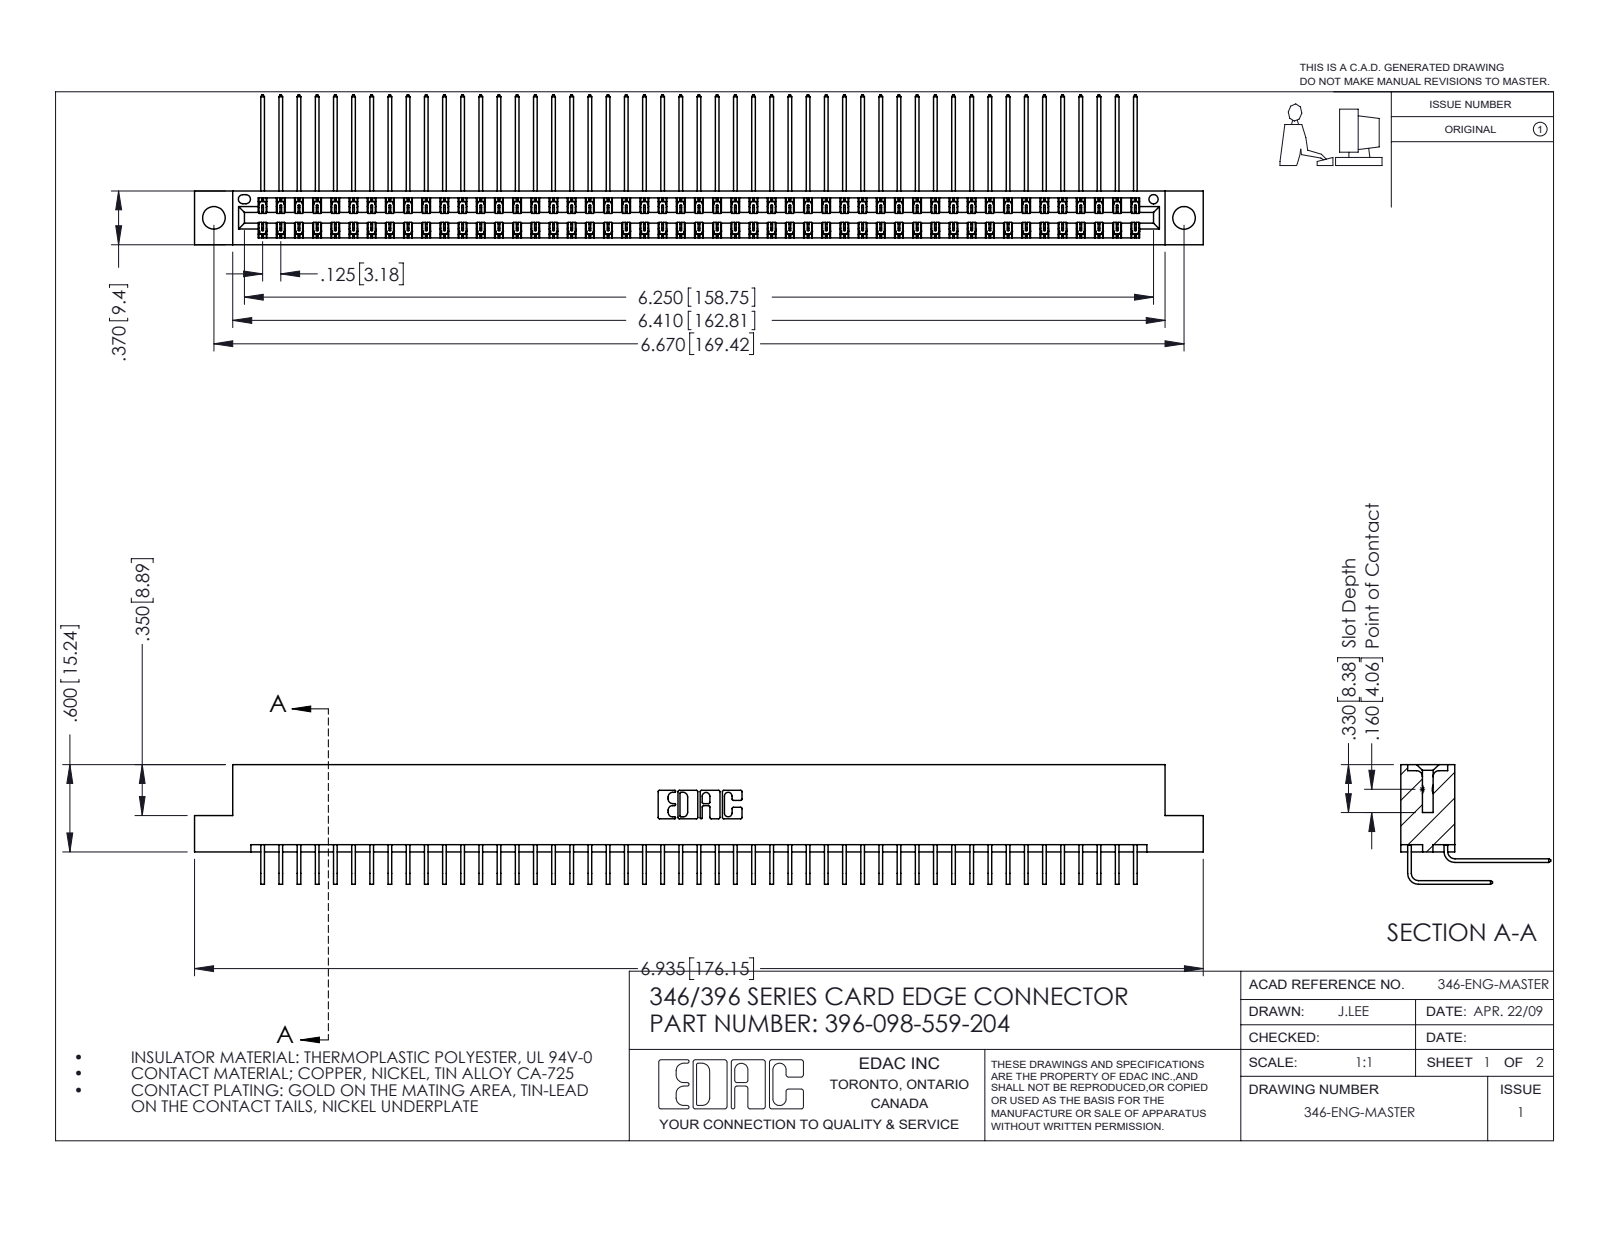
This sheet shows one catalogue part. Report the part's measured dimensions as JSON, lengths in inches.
{"part_name": "396-098-559-204; 346 Part_Flush Mounting Lugs - 0.156 Dia-TH; 345-292-001_559 Tail - 2; 345-292-001_558 559 Tail - 1", "step_written_by": "SolidWorks 2016 (CONFIG_CONTROL_DESIGN)", "units": "inches", "bodies": {"solids": 99, "faces": 5414, "planar": 3702, "cylindrical": 1712, "other": 0}, "overall_size": [6.935, 1.03, 0.823], "volume_in3": 1.081, "surface_area_in2": 41.81, "round_holes": [[0.156, 2], [0.064, 1]], "partial_cylinders_radius": [[0.006, 147], [0.01, 22], [0.007, 6], [0.031, 6], [0.026, 3], [0.014, 2], [0.022, 2], [0.024, 2]], "face_to_face_distances": [0.048, 0.322, 0.025, 0.37, 0.25, 0.072, 0.298, 0.275, 0.148, 0.222], "hole_center_spacings": [0.246, 6.461, 6.67]}
